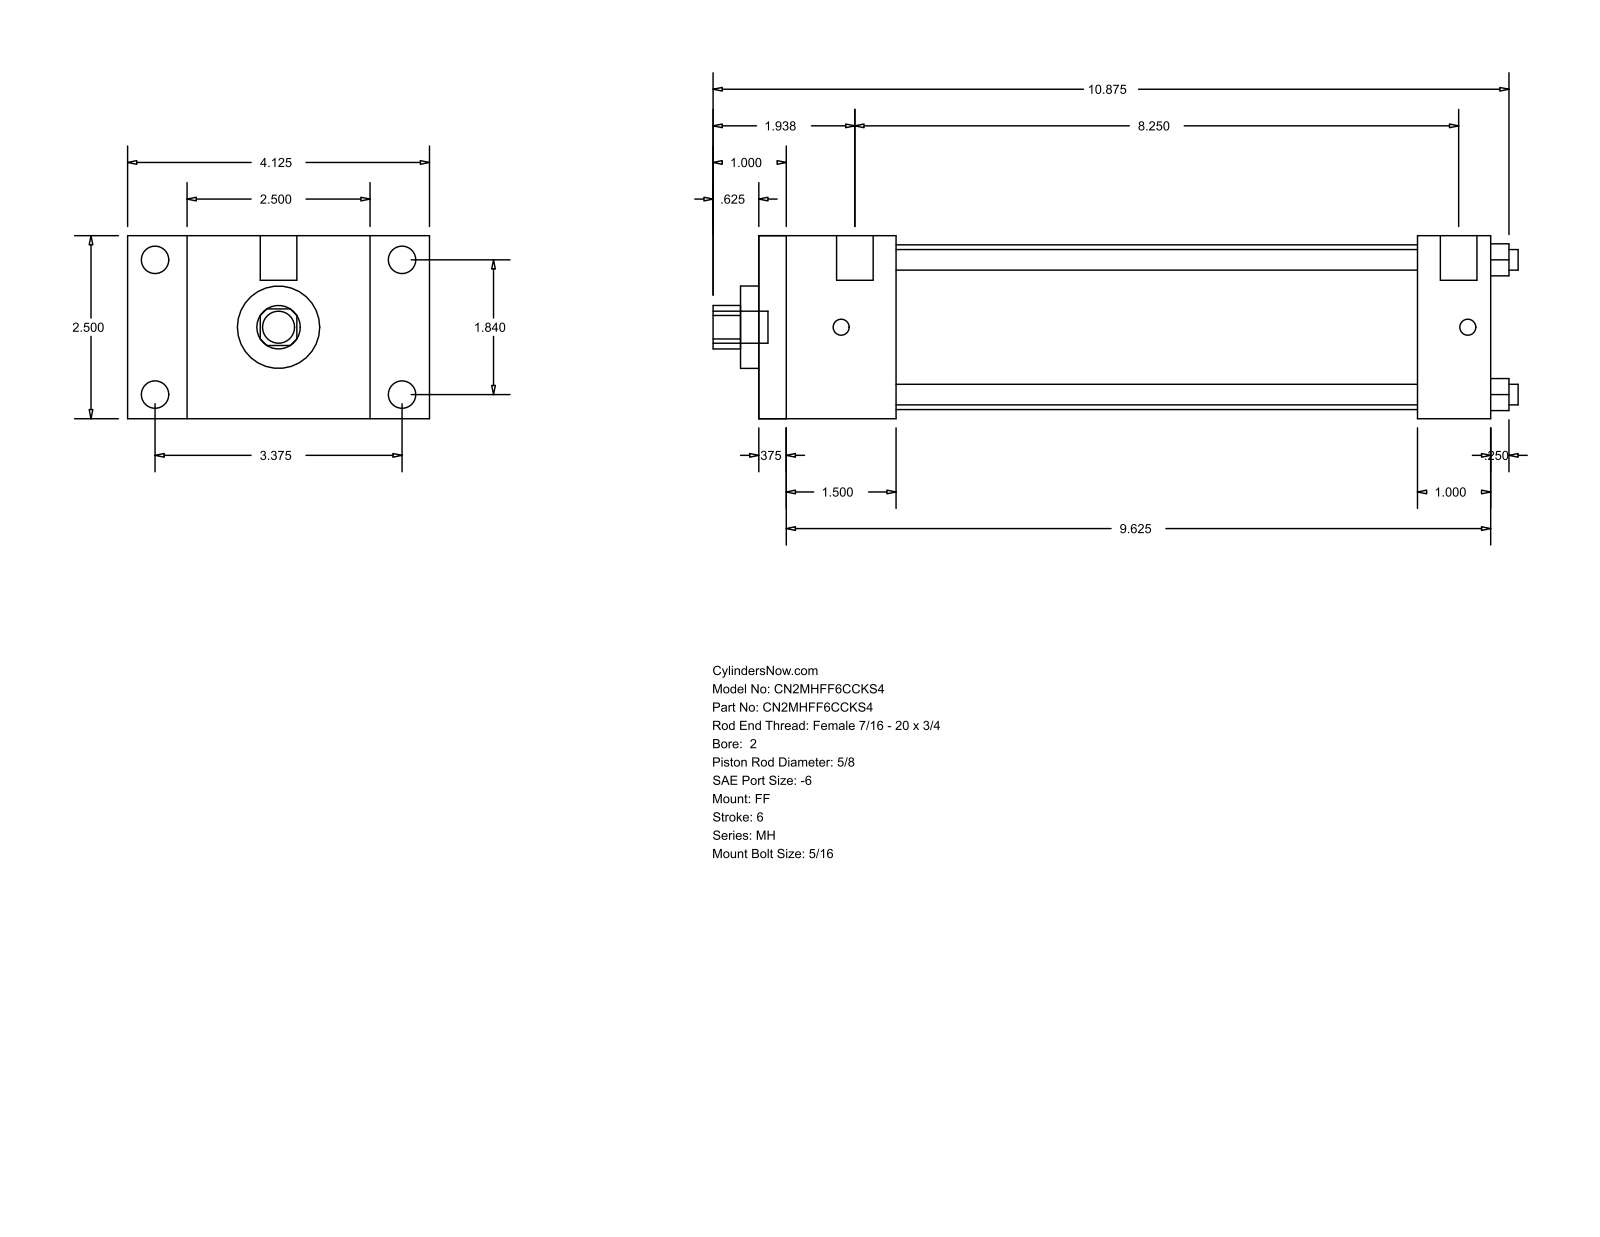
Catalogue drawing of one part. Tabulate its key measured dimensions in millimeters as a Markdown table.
| quantity | value |
| --- | --- |
| part name | MH_FF__0200_0.625 |
| STEP written by | GSSL Pune (CONFIG_CONTROL_DESIGN) |
| units | millimeters |
| bodies | 0 solids, 92 faces (64 planar, 28 cylindrical, 0 other) |
| overall size | 279.4 × 104.78 × 63.5 |
| round holes (diameter × count) | 7.14 × 4, 15.88 × 1, 28.57 × 1, 57.15 × 1 |
| round bosses / shafts (diameter × count) | 9.53 × 4, 5.56 × 4, 12.7 × 2, 11.11 × 1 |
| partial cylindrical surfaces (radius × count) | 7.54 × 1 |
| main face-to-face distances | 63.5, 254, 9.52, 244.48, 38.1, 47.62, 228.59, 219.07, 180.97, 206.38 |
| hole center spacings | 33.05, 46.74, 66.1 |
